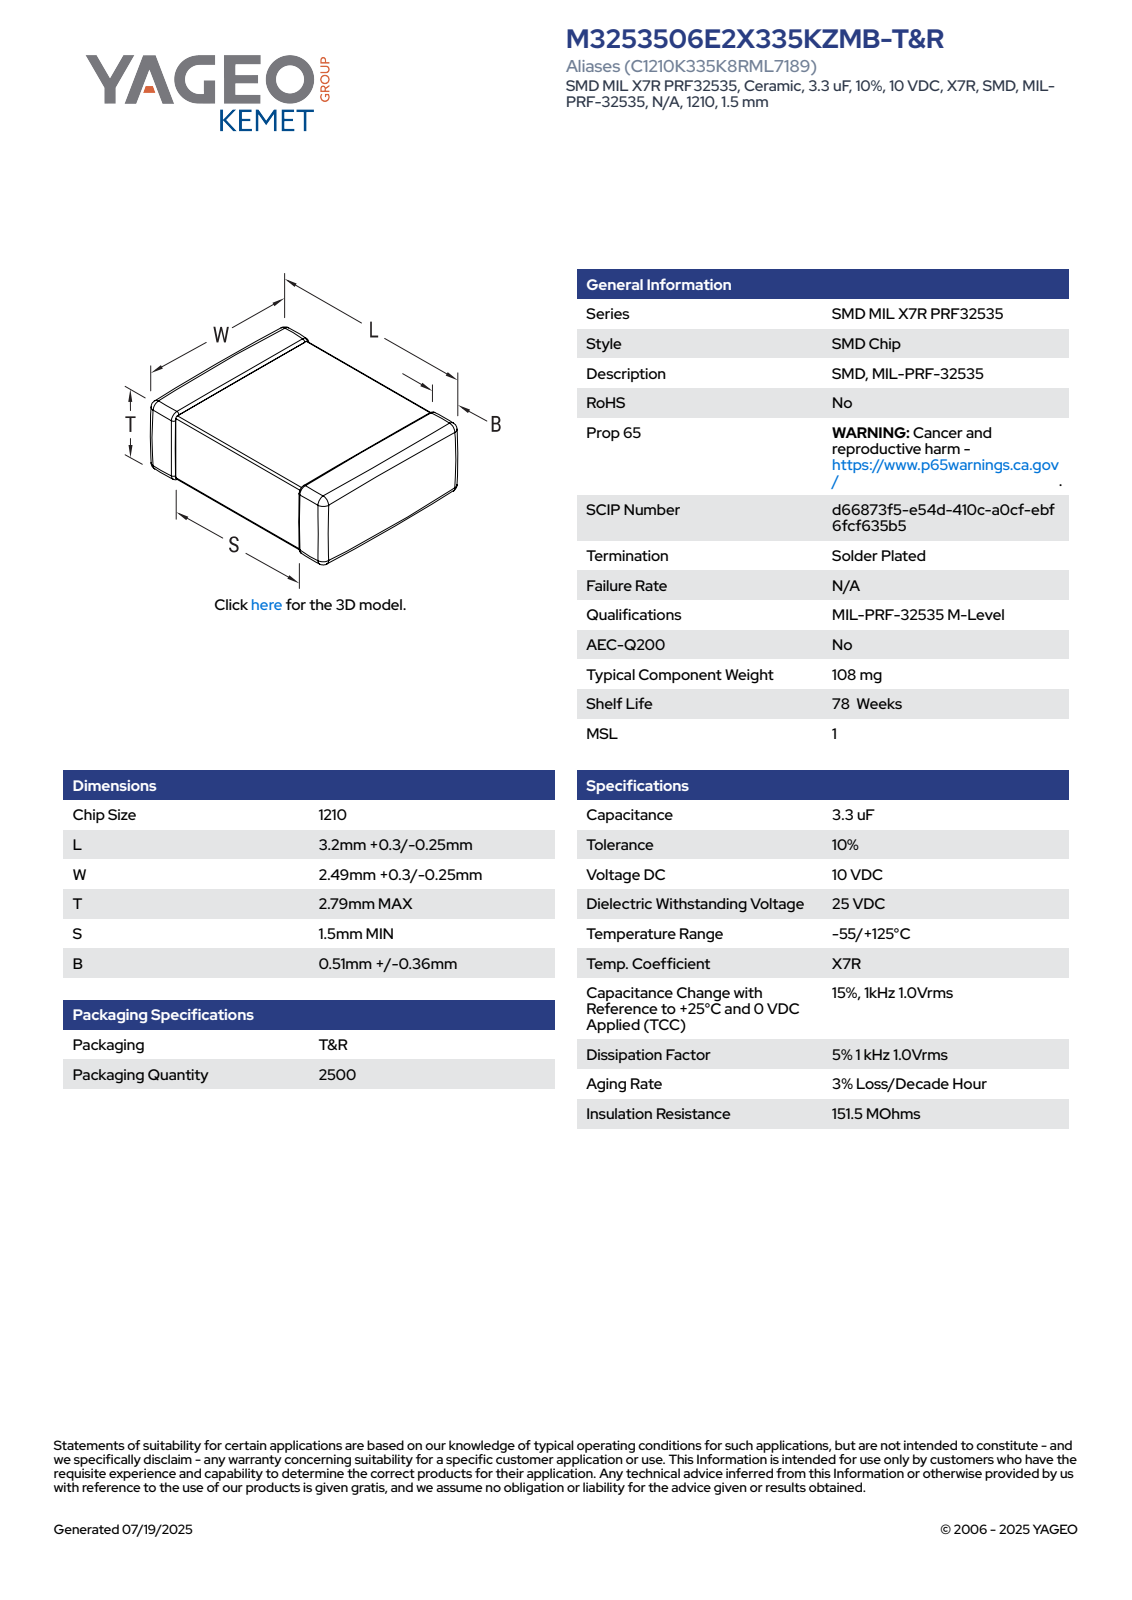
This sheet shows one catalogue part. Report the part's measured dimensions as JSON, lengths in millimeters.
{"part_name": "CCSM_STD_1210_L0.3W0.3T2.79S2.79B0.87", "step_written_by": "SolidWorks 2021 (AUTOMOTIVE_DESIGN)", "units": "millimeters", "bodies": {"solids": 4, "faces": 125, "planar": 71, "cylindrical": 38, "other": 16}, "overall_size": [3.5, 2.79, 2.79], "volume_mm3": 26, "surface_area_mm2": 55, "face_to_face_distances": [2.73, 2.67, 2.79, 3.5, 2.74, 2.68, 1.48, 2.02, 1.89, 0.41]}
